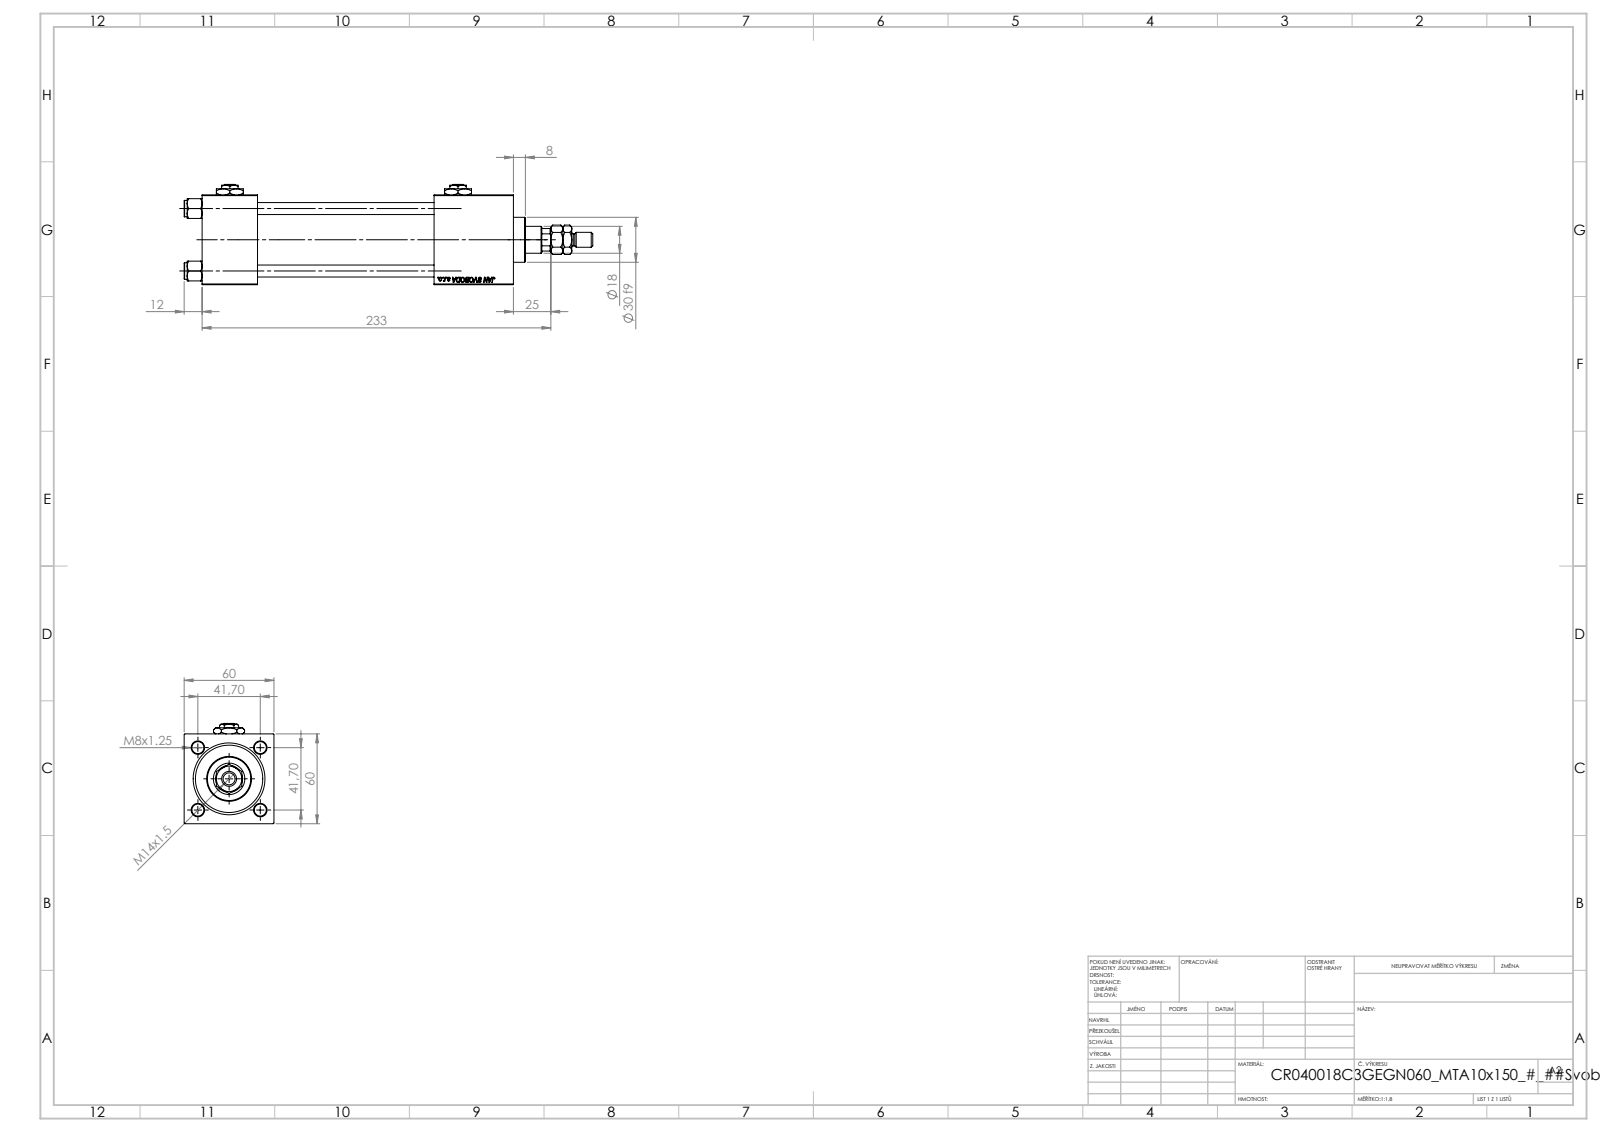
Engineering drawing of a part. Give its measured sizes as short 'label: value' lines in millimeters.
name: Zatka_pro_OIL_PORT; V215_VC_A; MTA; V215CR_C_TYCINKA (+3 more)
written by: SolidWorks 2019 (CONFIG_CONTROL_DESIGN)
unit: mm
bodies: 14 solids, 1299 faces (589 planar, 102 cylindrical, 608 other)
size: 273 × 67 × 60
volume: 454 975 mm³; area: 135 709 mm²
holes: 4× ⌀8, 2× ⌀7, 2× ⌀16.66, 2× ⌀24, 1× ⌀8.5, 1× ⌀18, 1× ⌀21, 1× ⌀31, 1× ⌀40, 1× ⌀45
bosses: 4× ⌀11, 1× ⌀46, 1× ⌀30, 1× ⌀10, 1× ⌀8
rounds: 1× R8.5
face distances: 60, 37, 208, 171, 53, 155, 118, 179.3, 142.3, 24.3
hole spacings: 29.49, 41.7, 58.97, 152.5
